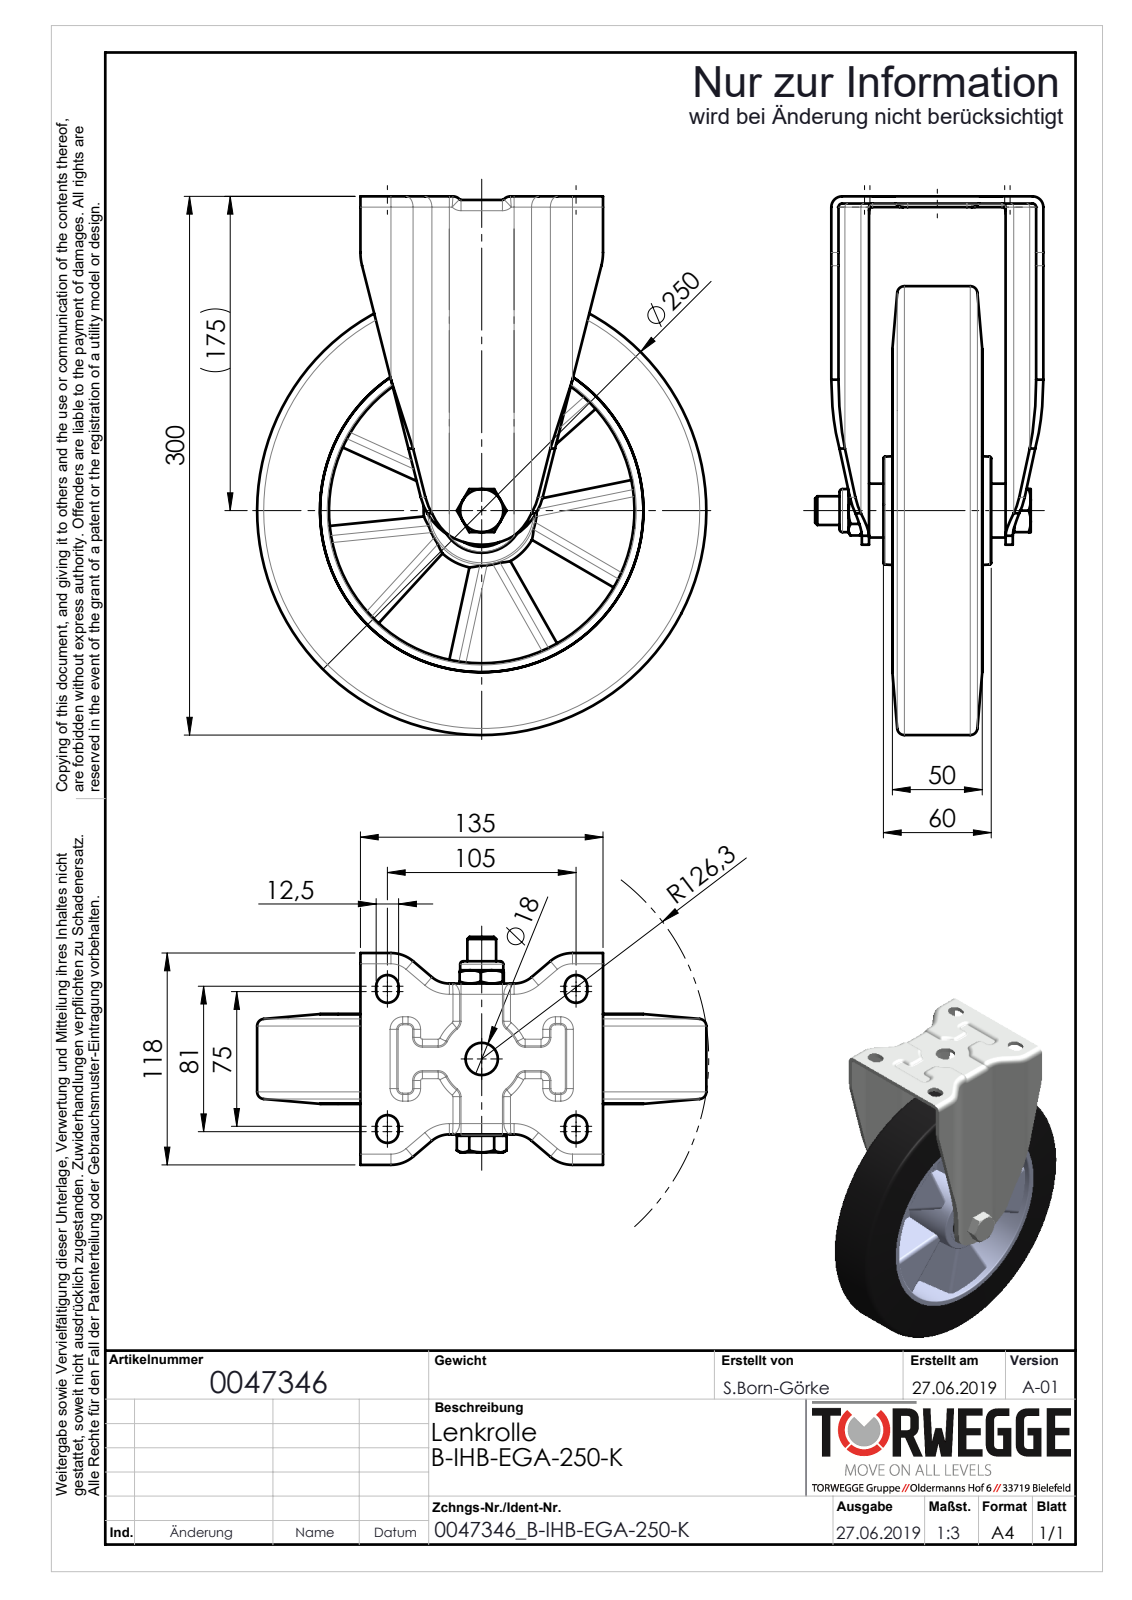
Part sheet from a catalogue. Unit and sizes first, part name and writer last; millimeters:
Units: millimetres
Overall size (bounding box): 300 × 250 × 127
Round holes (diameter × count): ⌀14 ×1, ⌀16 ×1, ⌀16.5 ×1, ⌀18 ×1, ⌀18.29 ×1, ⌀25 ×1, ⌀25.4 ×1, ⌀26 ×1, ⌀31.6 ×1, ⌀40.4 ×1, ⌀42 ×1, ⌀47 ×1
Round bosses / shafts (diameter × count): ⌀250 ×1, ⌀30 ×1, ⌀24 ×1
Partial cylindrical surfaces — rounded edges, fillets, slot ends (radius × count): R1 ×20, R4 ×20, R5 ×20, R2 ×10, R6 ×10, R6.25 ×8, R15 ×8, R19 ×8
Main face-to-face distances: 4, 23, 57, 80, 34, 53, 27, 19, 61, 17
Volume: 1 759 000 mm³ · Surface area: 415 602 mm²
Bodies: 15 solids, 598 faces (138 planar, 246 cylindrical, 214 other)
Part name (STEP PRODUCT): 0047346_B-IHB-EGA-250-K_(A-01)
STEP written by: SolidWorks 2018 (AUTOMOTIVE_DESIGN)
